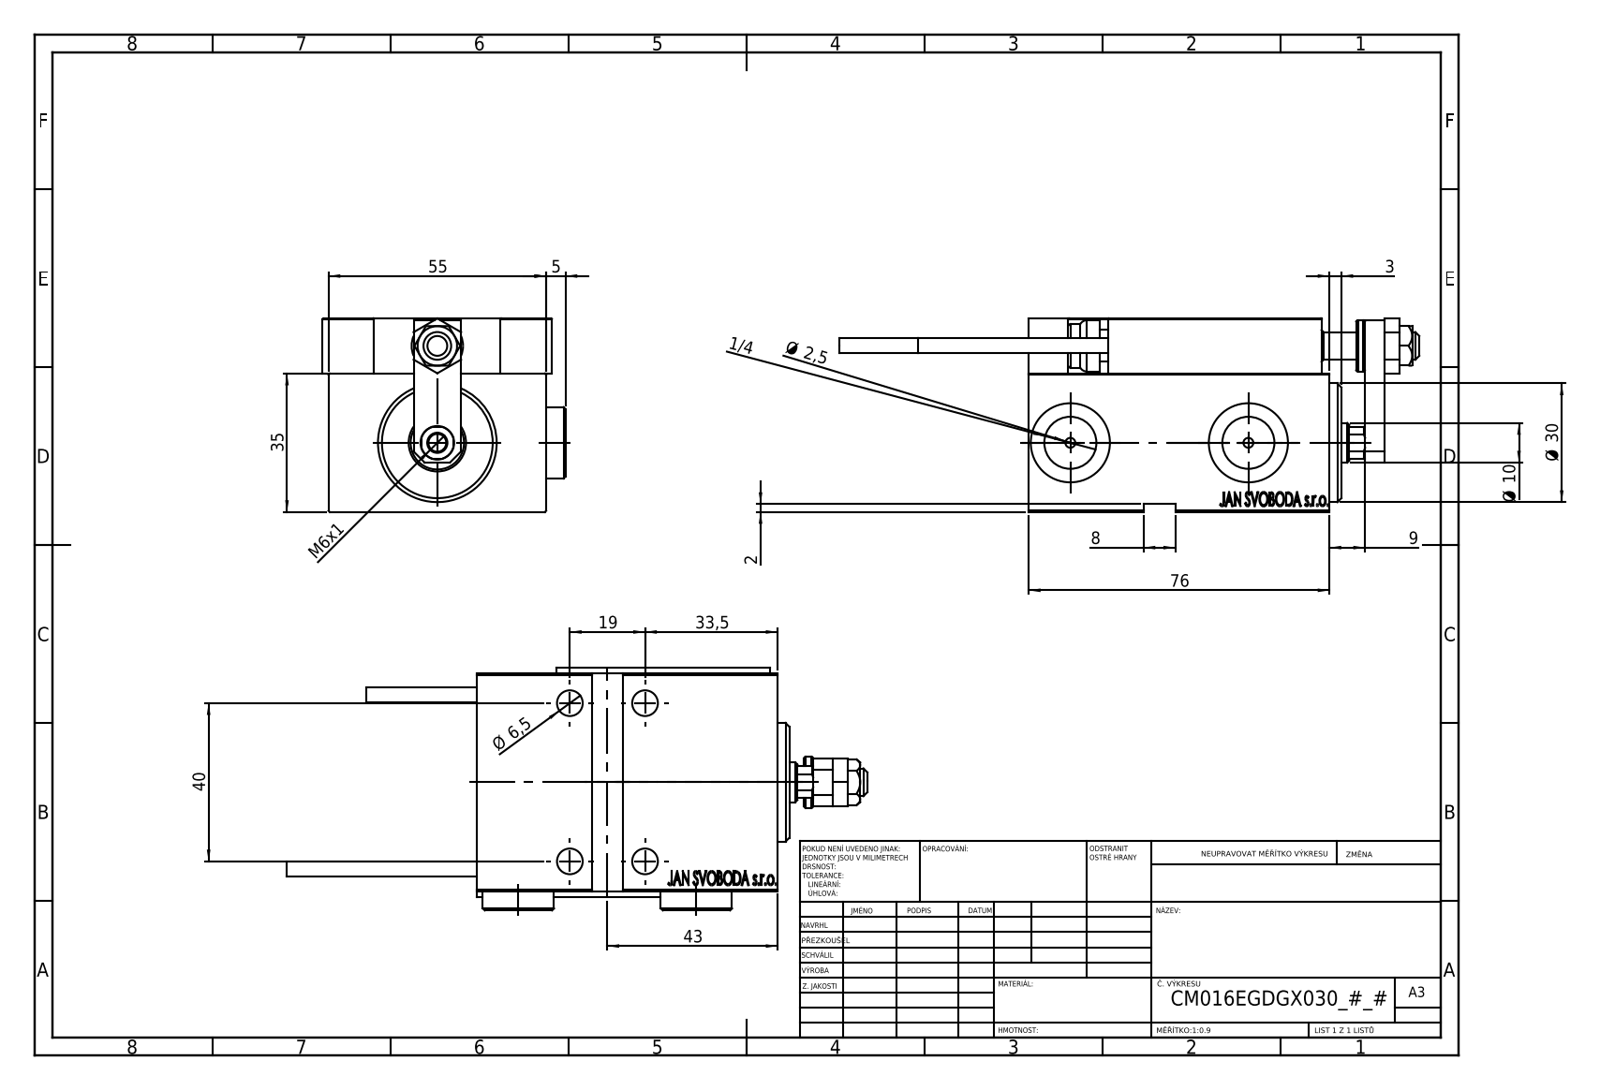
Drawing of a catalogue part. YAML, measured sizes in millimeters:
part_name: "Zatka_OIL_PORT; SWITCH DIM B,W; V450CM_E_Body; V450CM_E_VCP (+7 more)"
step_written_by: "SolidWorks 2019 (CONFIG_CONTROL_DESIGN)"
units: millimeters
bodies: {solids: 26, faces: 1350, planar: 605, cylindrical: 200, other: 545}
overall_size: [146.7, 61.4, 49]
volume: 176176
surface_area: 57480
round_holes:
  - {diameter: 8, count: 5}
  - {diameter: 3.2, count: 4}
  - {diameter: 4, count: 4}
  - {diameter: 6.5, count: 4}
  - {diameter: 10.5, count: 4}
  - {diameter: 2.5, count: 2}
  - {diameter: 5, count: 2}
  - {diameter: 13.16, count: 2}
  - {diameter: 20, count: 2}
  - {diameter: 4.5, count: 1}
  - {diameter: 7, count: 1}
  - {diameter: 8.5, count: 1}
round_bosses_or_shafts:
  - {diameter: 18, count: 3}
  - {diameter: 5, count: 2}
  - {diameter: 3.8, count: 2}
  - {diameter: 30, count: 1}
  - {diameter: 13, count: 1}
  - {diameter: 11, count: 1}
partial_cylinders:
  - {radius: 0.3, count: 30}
  - {radius: 3, count: 2}
  - {radius: 4.5, count: 1}
face_to_face_distances: [35, 14, 5, 49, 10, 55, 1.5, 3, 20, 7]
hole_center_spacings: [11.37, 12.42, 19, 20, 21.03, 28.07, 28.32, 29.59]
